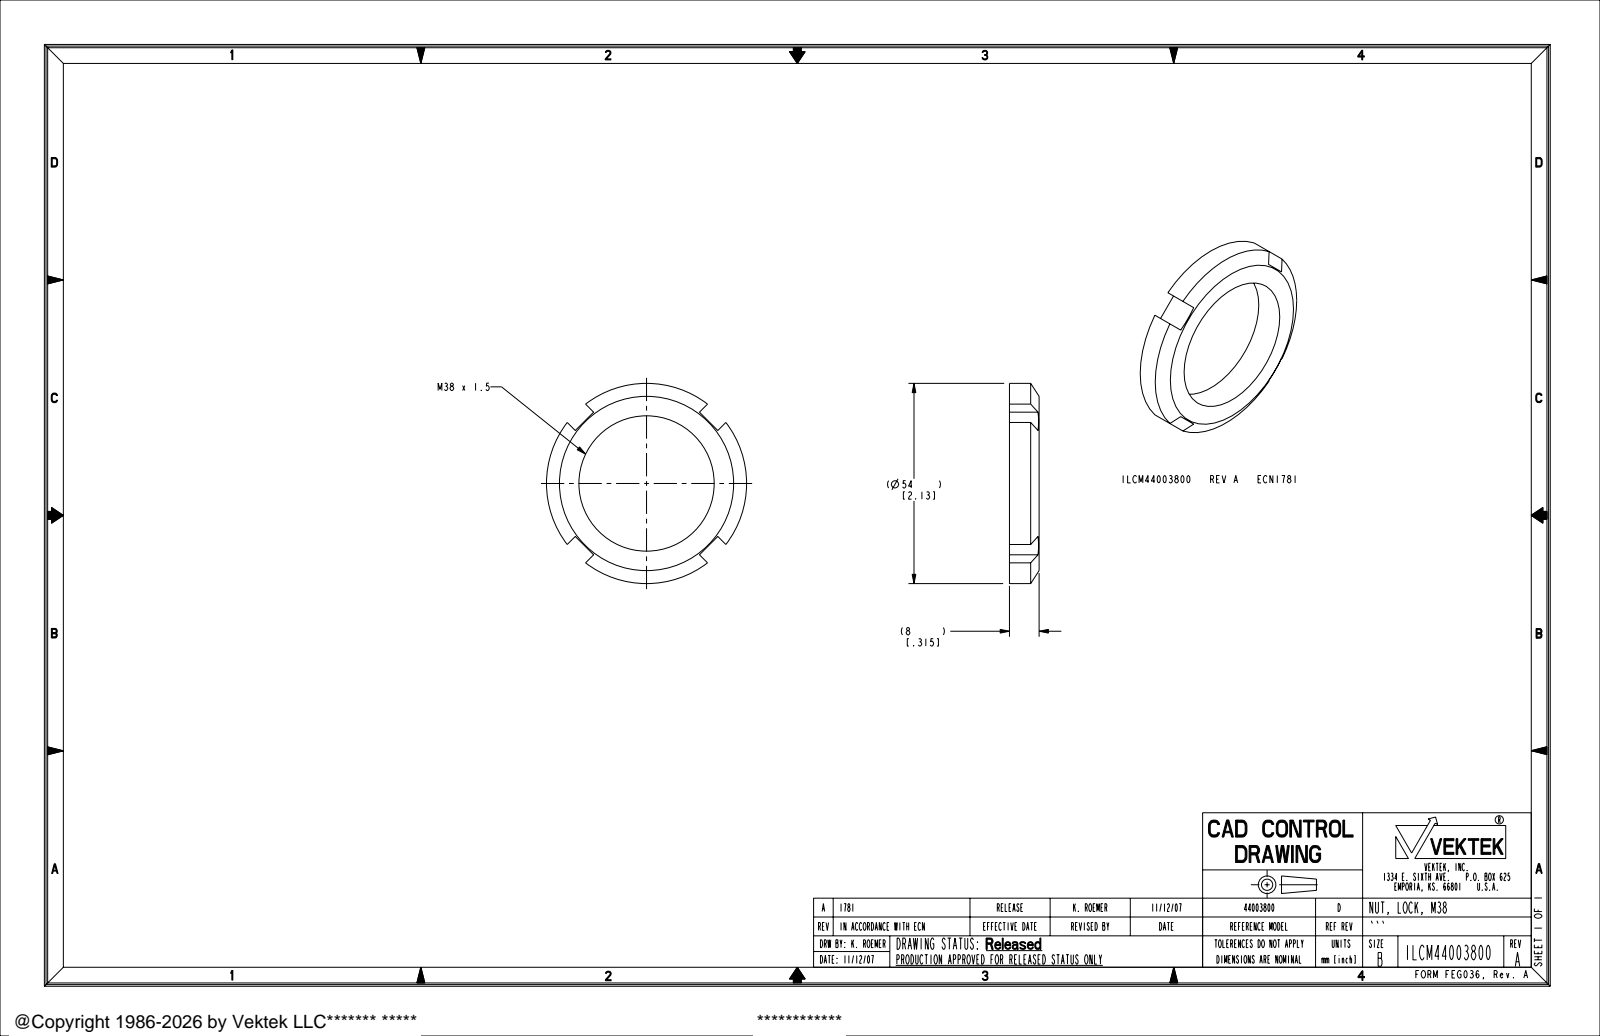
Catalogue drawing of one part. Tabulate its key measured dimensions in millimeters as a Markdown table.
| quantity | value |
| --- | --- |
| part name | ILCM44003800 |
| STEP written by | PRO/ENGINEER BY PARAMETRIC TECHNOLOGY CORPORATION, 2005180 (AUTOMOTIVE_DESIGN_CC2) |
| units | millimeters |
| bodies | 1 solid, 22 faces (14 planar, 6 cylindrical, 2 other) |
| overall size | 54 × 54 × 8 |
| volume | 8 694 mm³ |
| surface area | 4 509 mm² |
| round holes (diameter × count) | 36.5 × 1 |
| round bosses / shafts (diameter × count) | 54 × 1 |
| main face-to-face distances | 8, 20.2, 27.2, 47.4, 7 |
